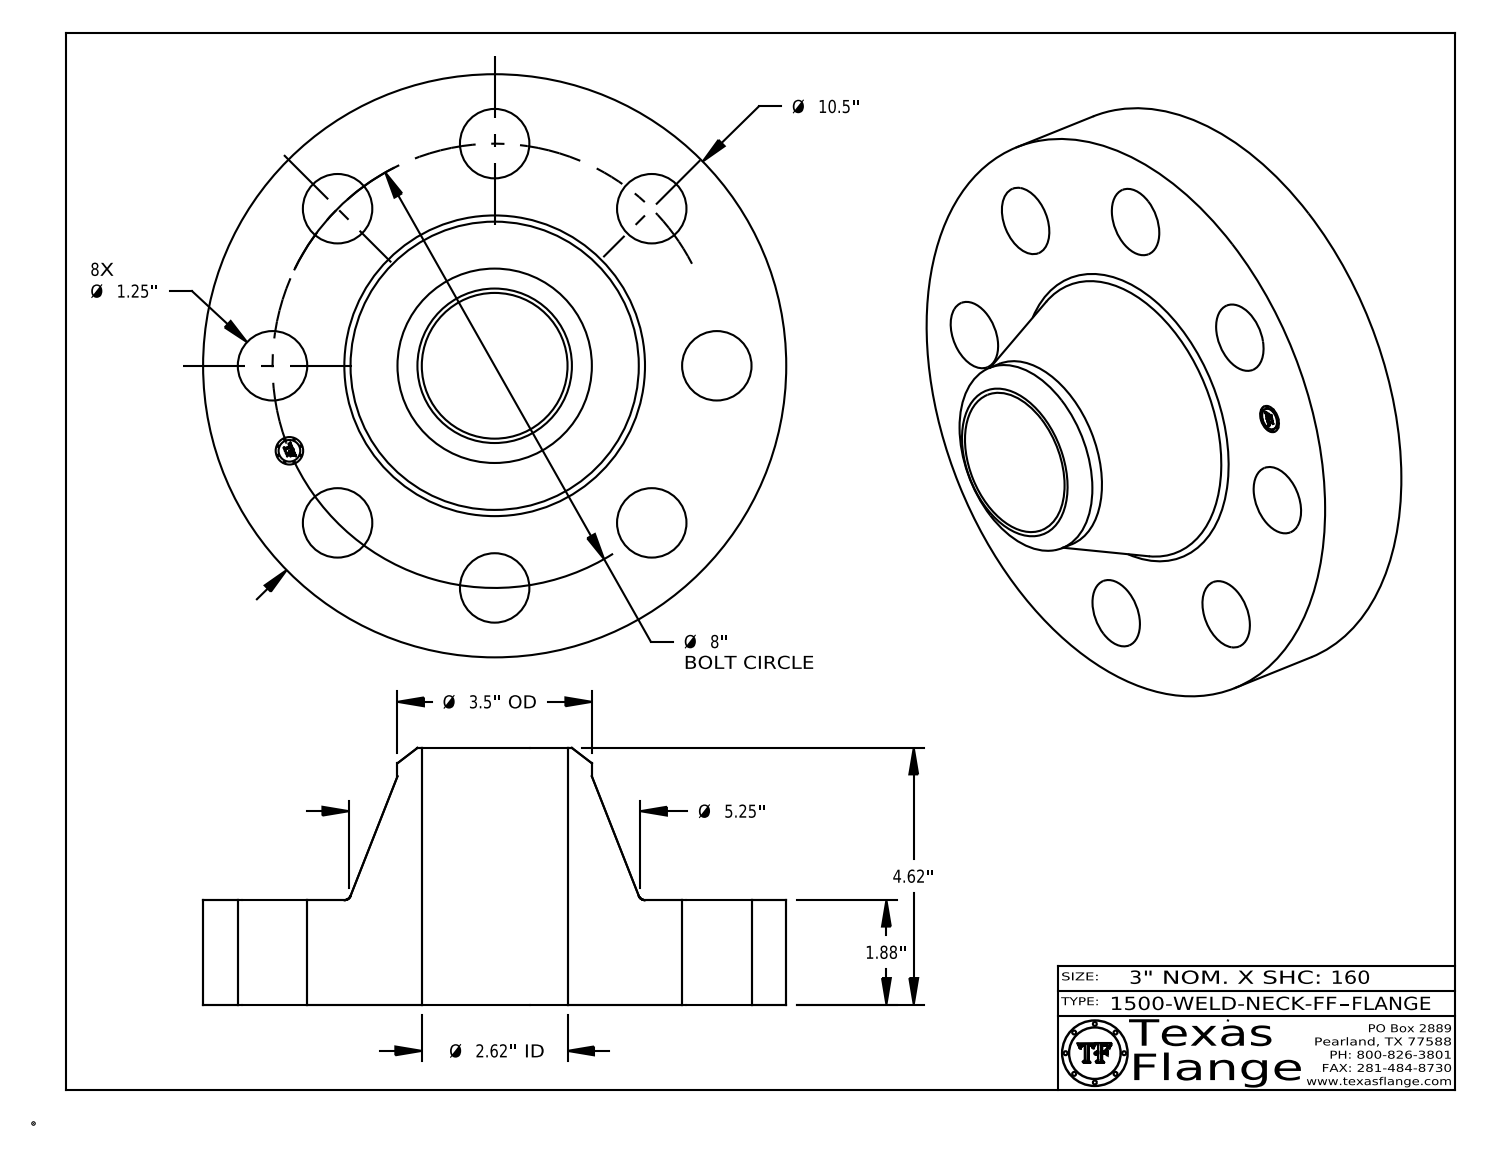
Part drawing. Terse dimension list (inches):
name: 1500-WELD-NECK-FF
written by: CATIA V5 STEP AP214 (AUTOMOTIVE_DESIGN)
unit: in
bodies: 1 solid, 416 faces (368 planar, 42 cylindrical, 6 other)
size: 10.5 × 10.5 × 4.62
volume: 157.7 in³; area: 326.1 in²
holes: 8× ⌀1.25, 1× ⌀0.495, 1× ⌀2.624
bosses: 8× ⌀0.03, 1× ⌀10.5, 1× ⌀3.5, 1× ⌀0.39
face distances: 1.88, 4.62, 2.74, 0.015, 1.865, 2.755, 0.148, 0.145, 0.027, 0.096
hole spacings: 4, 3.061, 5.657, 7.391, 1.561, 6.652, 7.846, 8
